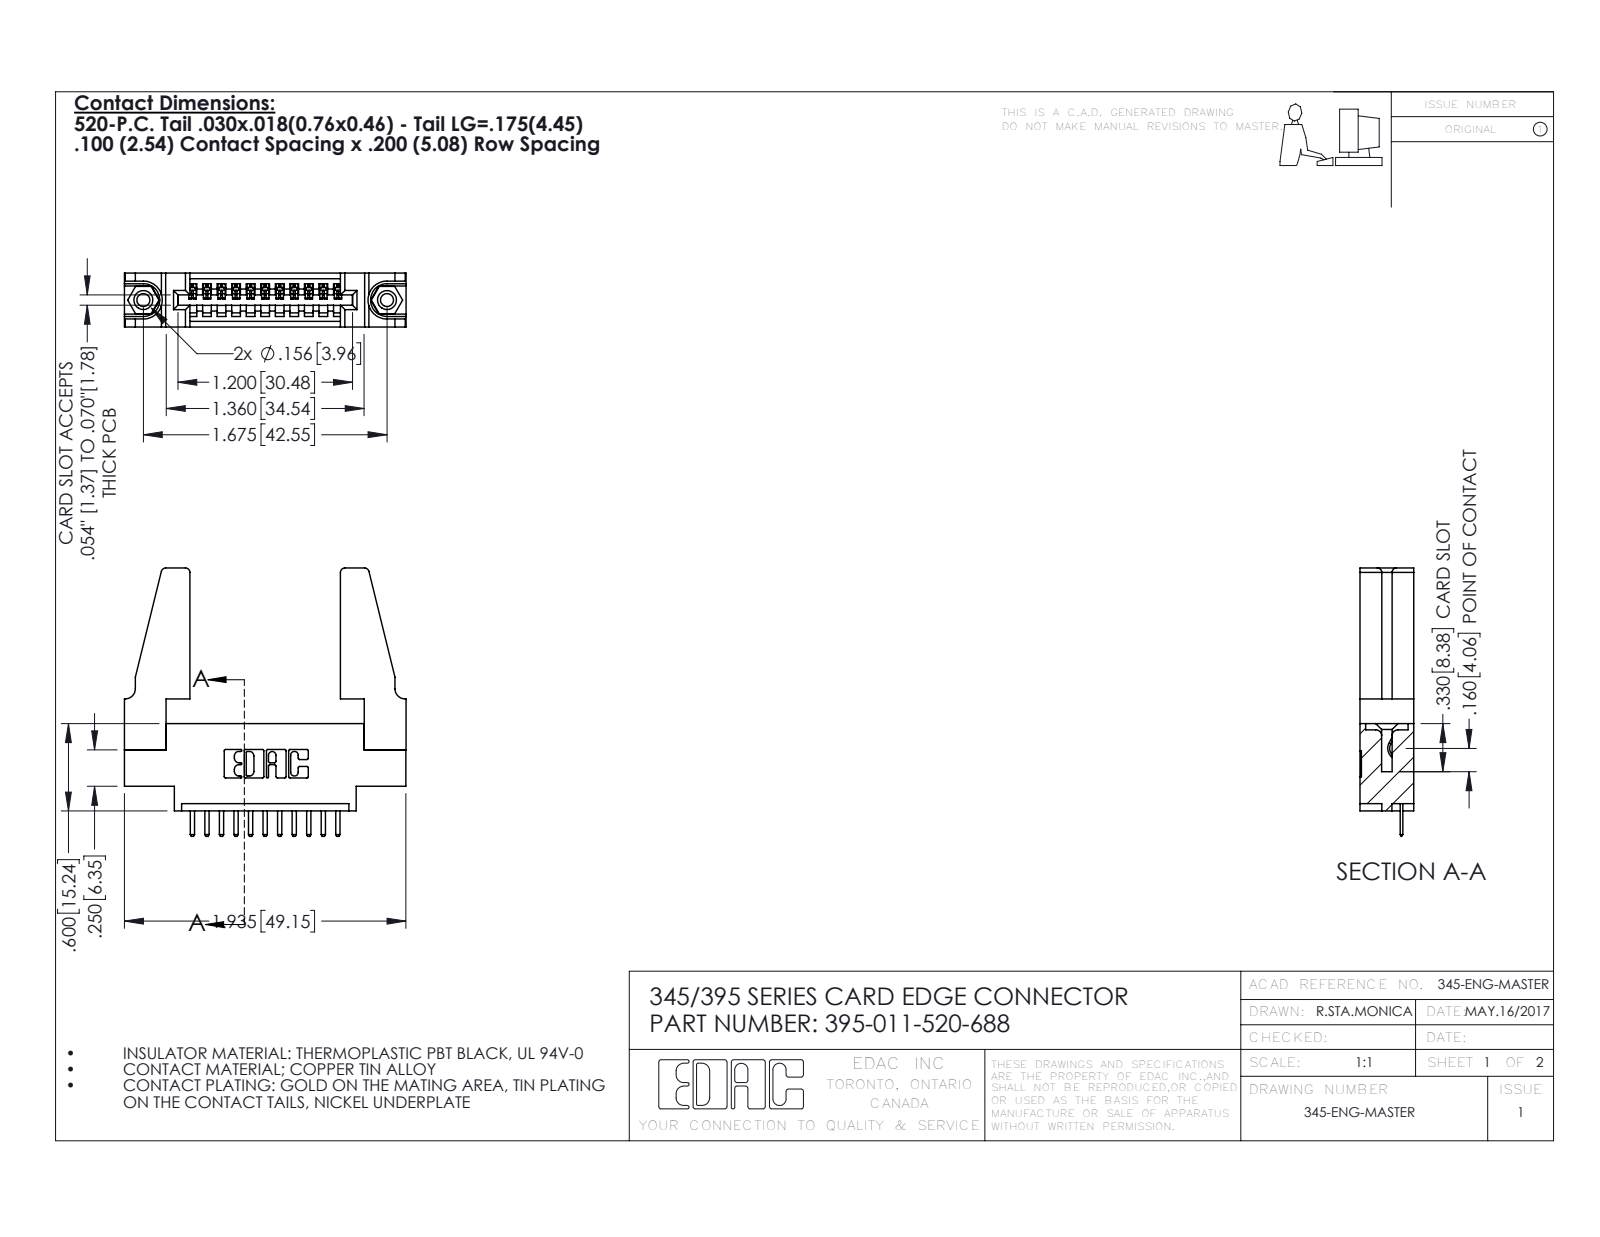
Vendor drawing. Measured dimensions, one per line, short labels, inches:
name: 345-250-001_345-250-001-102; 345 Part_0.170 Offset - 0.156 Dia-TH; 345-220-078_345-220-088; 395-011-520-688 (+1 more)
written by: SolidWorks 2016 (CONFIG_CONTROL_DESIGN)
unit: in
bodies: 16 solids, 936 faces (618 planar, 302 cylindrical, 16 other)
size: 1.936 × 1.845 × 0.37
volume: 0.459 in³; area: 13.03 in²
holes: 2× ⌀0.089, 2× ⌀0.125, 2× ⌀0.156, 1× ⌀0.064
bosses: 2× ⌀0.155
rounds: 24× R0.01, 22× R0.006, 22× R0.01, 8× R0.03, 6× R0.007, 6× R0.031, 3× R0.026, 2× R0.031
face distances: 0.37, 0.072, 0.298, 0.2, 0.098, 0.272, 0.025, 0.225, 0.148, 0.15
hole spacings: 0.27, 1.443, 1.675
